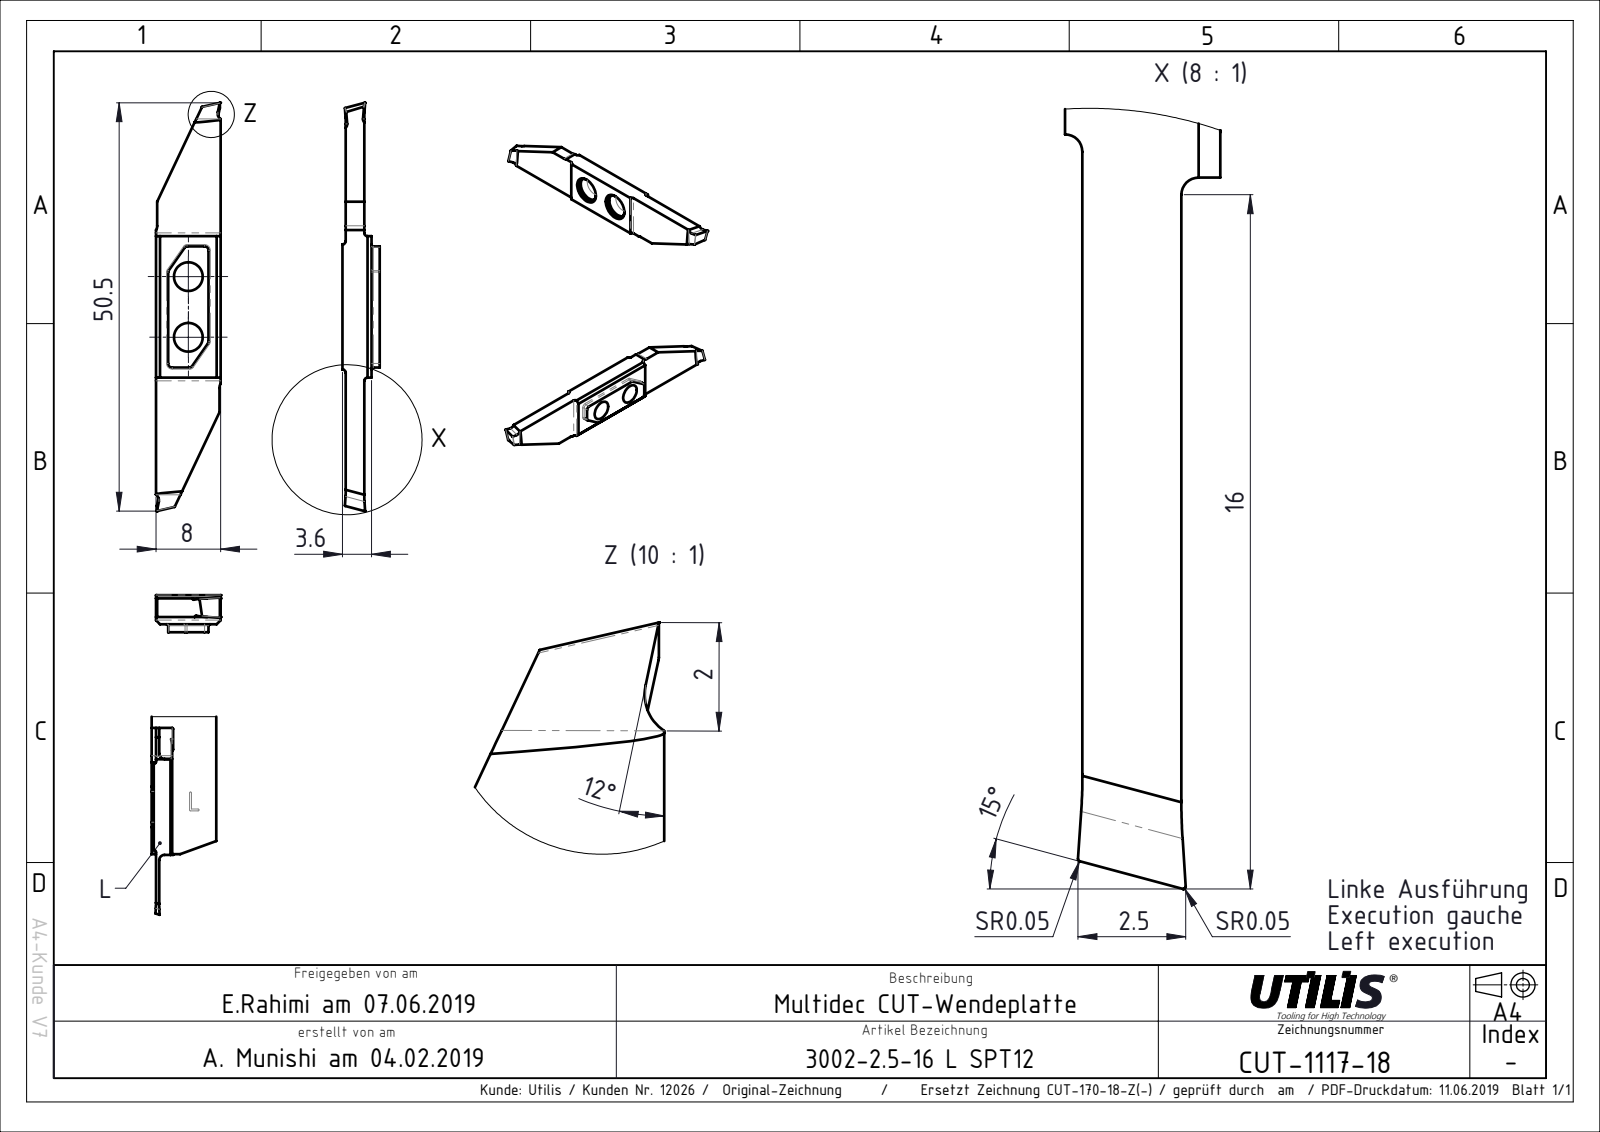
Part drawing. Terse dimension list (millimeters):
name: CUT-1117; ASME Y14.5
written by: FormatWorks Professional (AP242_MANAGED_MODEL_BASED_3D_ENGINEERING_MIM_LF)
unit: mm
bodies: 1 solid, 40 faces (24 planar, 16 cylindrical, 0 other)
size: 50.5 × 8 × 3.6
volume: 855 mm³; area: 991 mm²
holes: 2× ⌀3.55
rounds: 4× R0.4, 2× R1
face distances: 2.3, 0.4, 2.7, 3.6, 3.2, 0.9, 8, 18.09, 7.85, 7.7
hole spacings: 7.5
